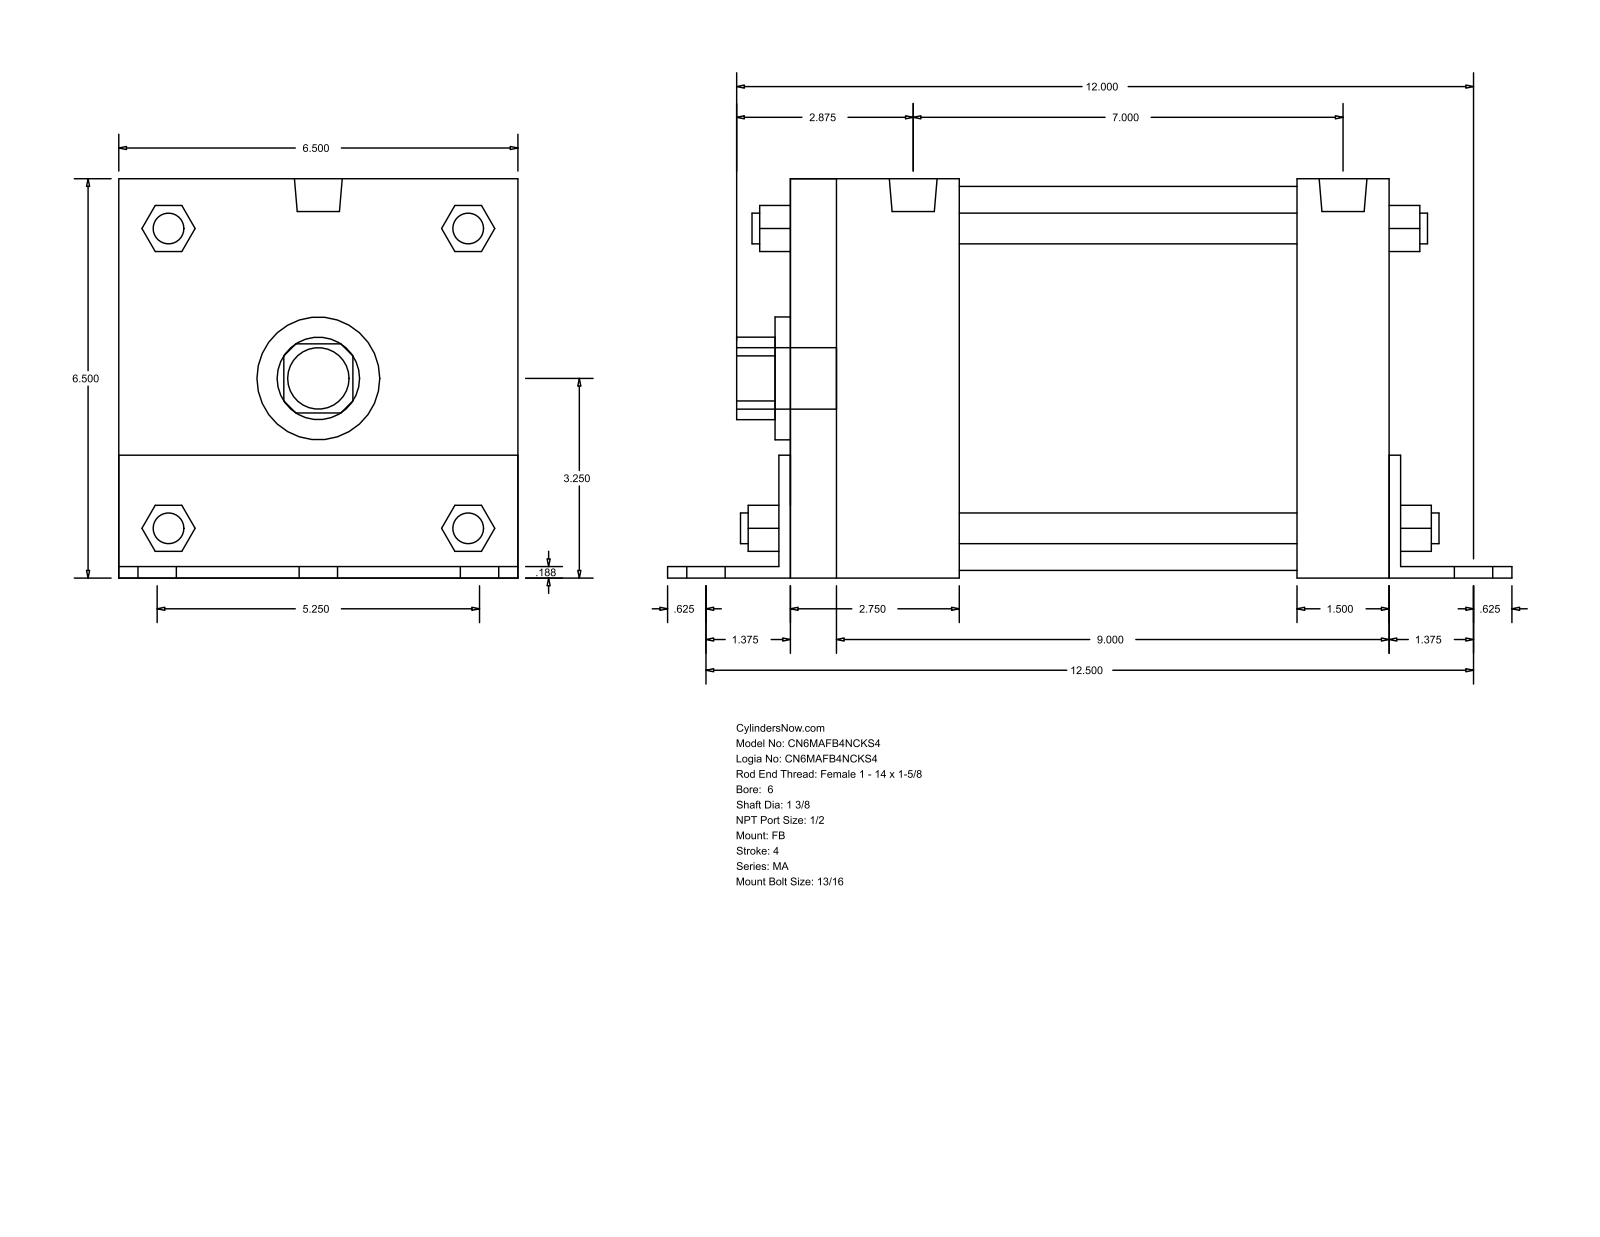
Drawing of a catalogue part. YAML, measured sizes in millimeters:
part_name: "MA_FB__0600_1.375"
step_written_by: "GSSL Pune (CONFIG_CONTROL_DESIGN)"
units: millimeters
bodies: {solids: 0, faces: 140, planar: 105, cylindrical: 35, other: 0}
overall_size: [346.07, 165.15, 165.1]
round_holes:
  - {diameter: 34.92, count: 1}
  - {diameter: 50.8, count: 1}
  - {diameter: 158.75, count: 1}
round_bosses_or_shafts:
  - {diameter: 20.64, count: 6}
  - {diameter: 17.46, count: 4}
  - {diameter: 12.7, count: 4}
  - {diameter: 19.77, count: 2}
  - {diameter: 25.4, count: 1}
partial_cylinders:
  - {radius: 17.06, count: 1}
  - {radius: 32.05, count: 1}
face_to_face_distances: [165.1, 4.76, 244.47, 165.15, 4.71, 160.39, 4.77, 38.1, 249.24, 254]
